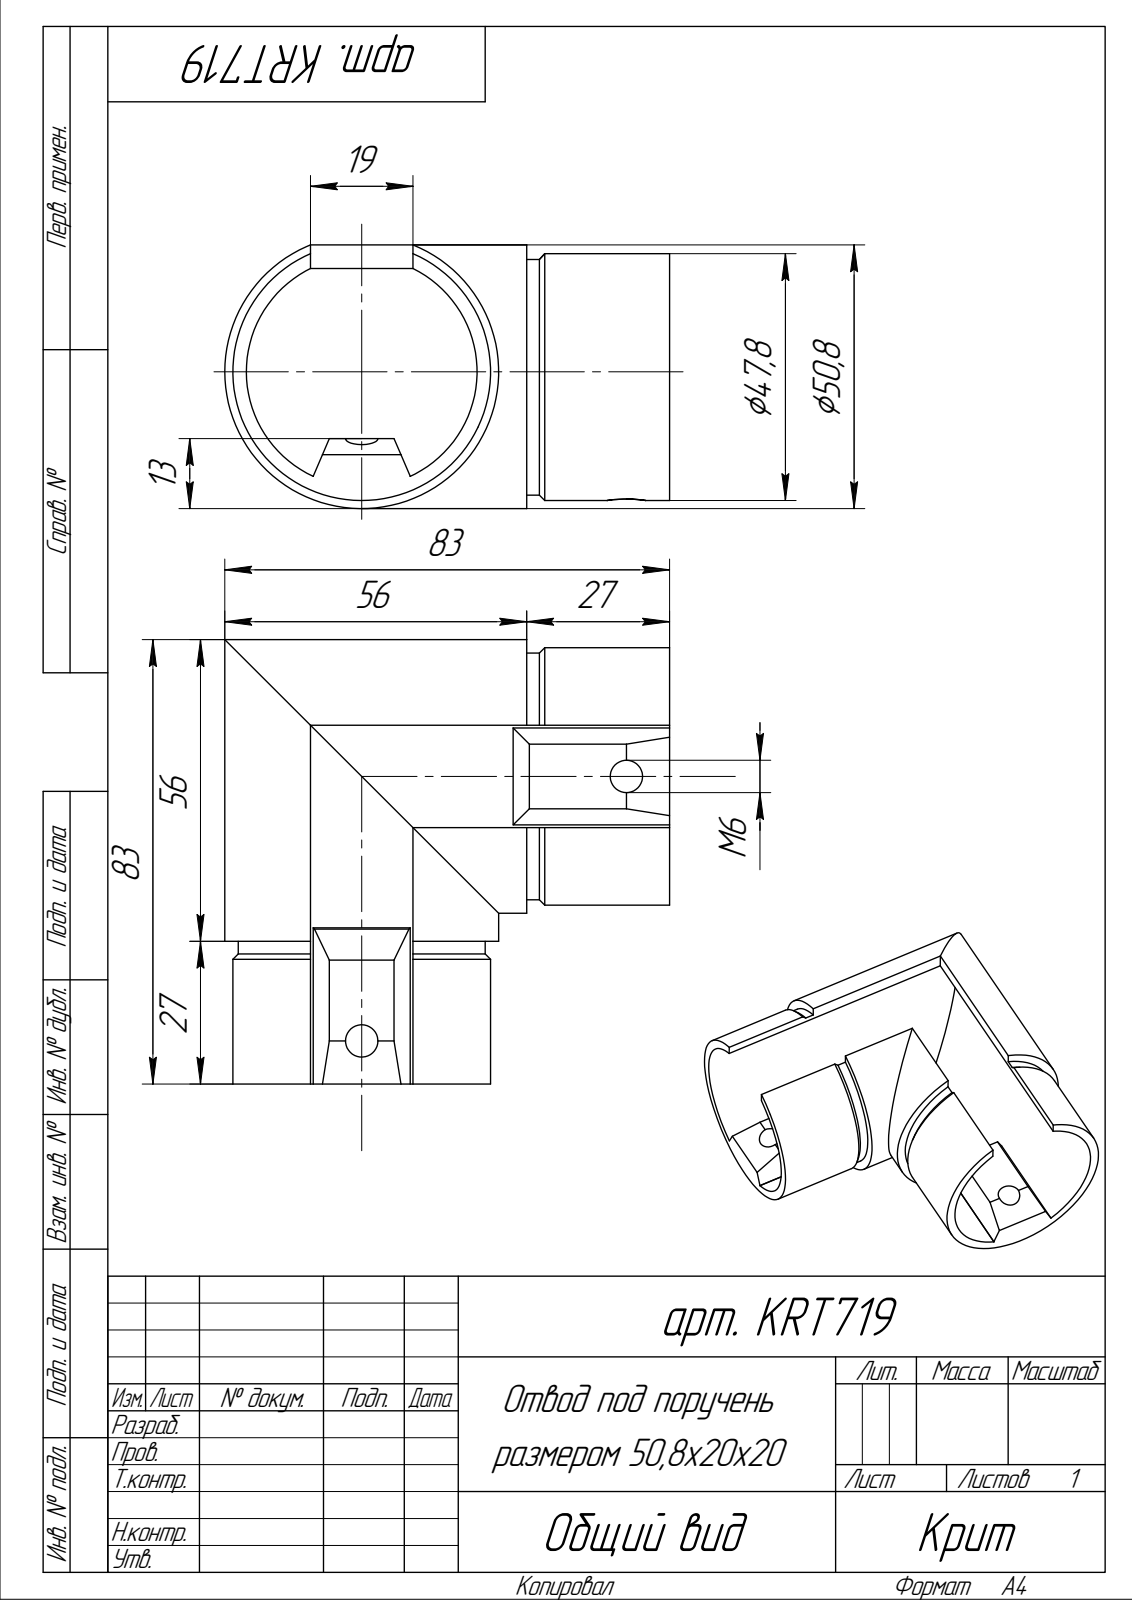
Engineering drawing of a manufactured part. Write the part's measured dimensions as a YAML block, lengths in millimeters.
part_name: "Отвод под поручень размером 50,8х20х20"
step_written_by: "ASCON Math Kernel (AUTOMOTIVE_DESIGN)"
units: millimeters
bodies: {solids: 1, faces: 39, planar: 25, cylindrical: 10, other: 4}
overall_size: [82.5, 82.5, 48.96]
volume: 52845
surface_area: 31842
round_holes:
  - {diameter: 6, count: 2}
  - {diameter: 42.8, count: 2}
round_bosses_or_shafts:
  - {diameter: 50.8, count: 2}
  - {diameter: 47.8, count: 2}
  - {diameter: 45.8, count: 2}
face_to_face_distances: [26.5, 40.1, 66.6, 19, 21.1, 47.6, 34.09, 37.6, 18.6, 2.5]
hole_center_spacings: [69.44]
